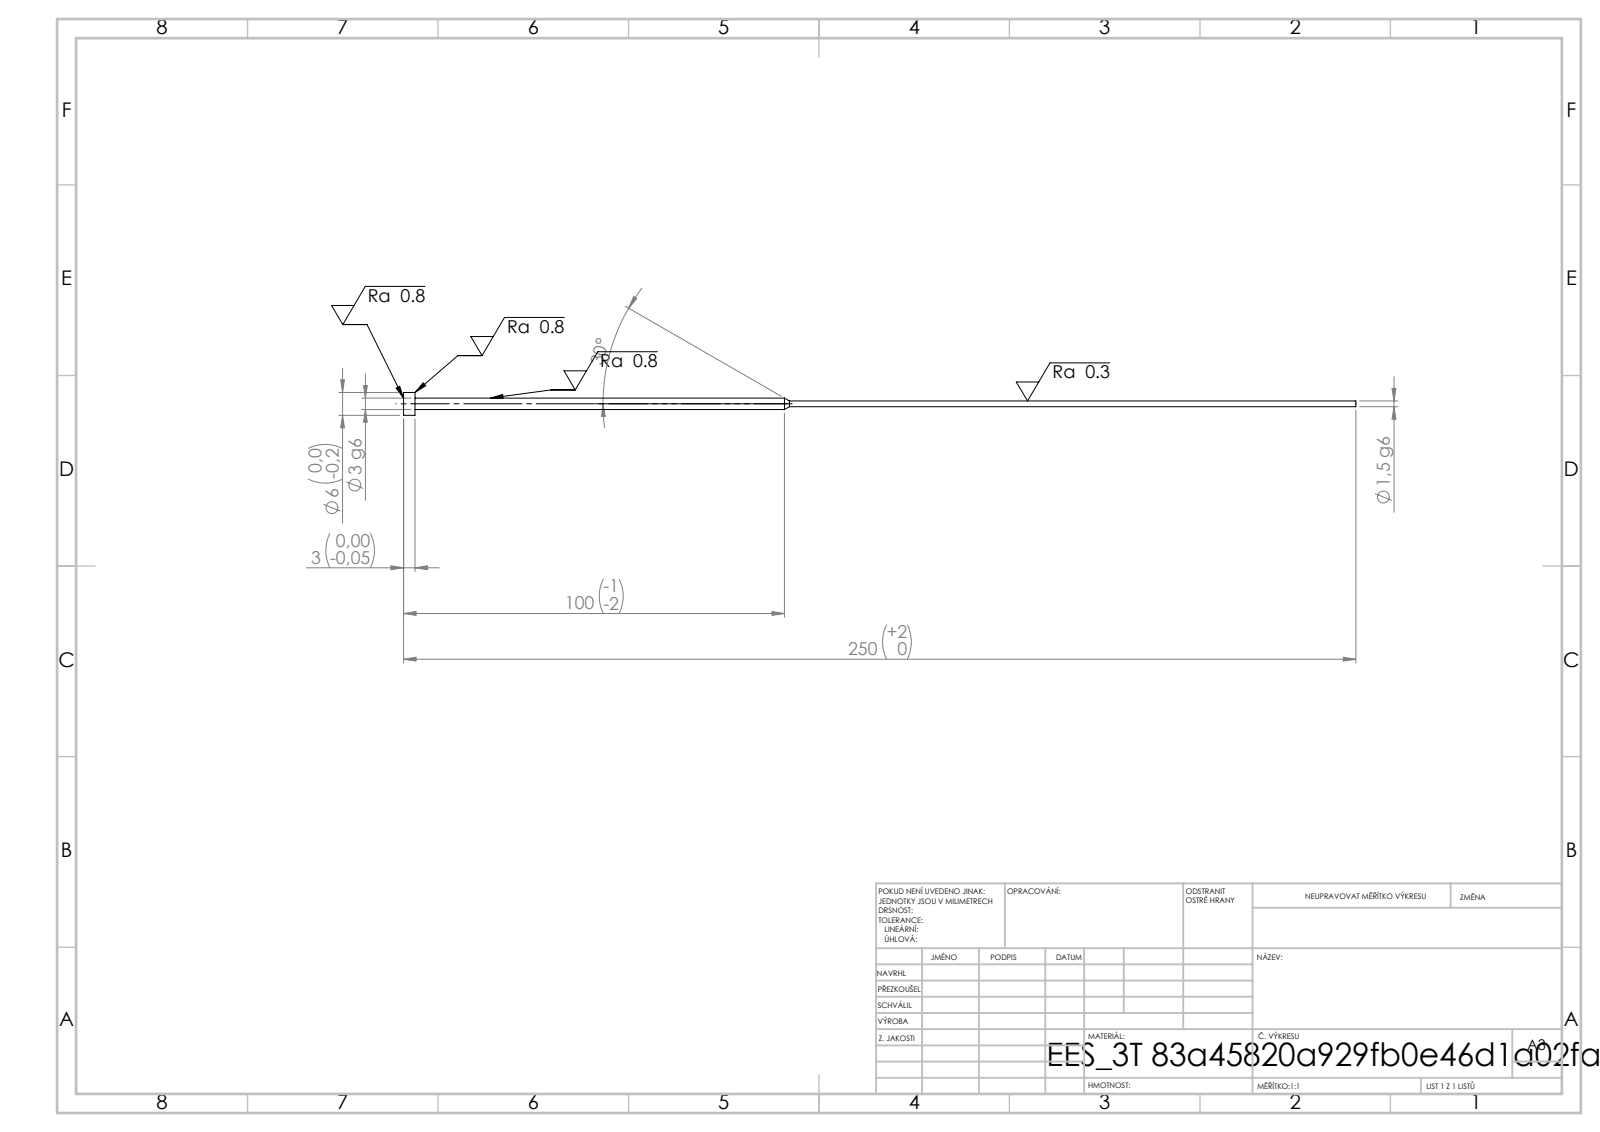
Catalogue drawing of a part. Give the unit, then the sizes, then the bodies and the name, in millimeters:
Units: millimetres
Overall size (bounding box): 250 × 6 × 6
Round bosses / shafts (diameter × count): ⌀6 ×1, ⌀3 ×1, ⌀1.5 ×1
Main face-to-face distances: 3, 247, 250
Volume: 1 039 mm³ · Surface area: 1 733 mm²
Bodies: 1 solid, 11 faces (3 planar, 6 cylindrical, 2 other)
STEP written by: SolidWorks 2019 (CONFIG_CONTROL_DESIGN)
